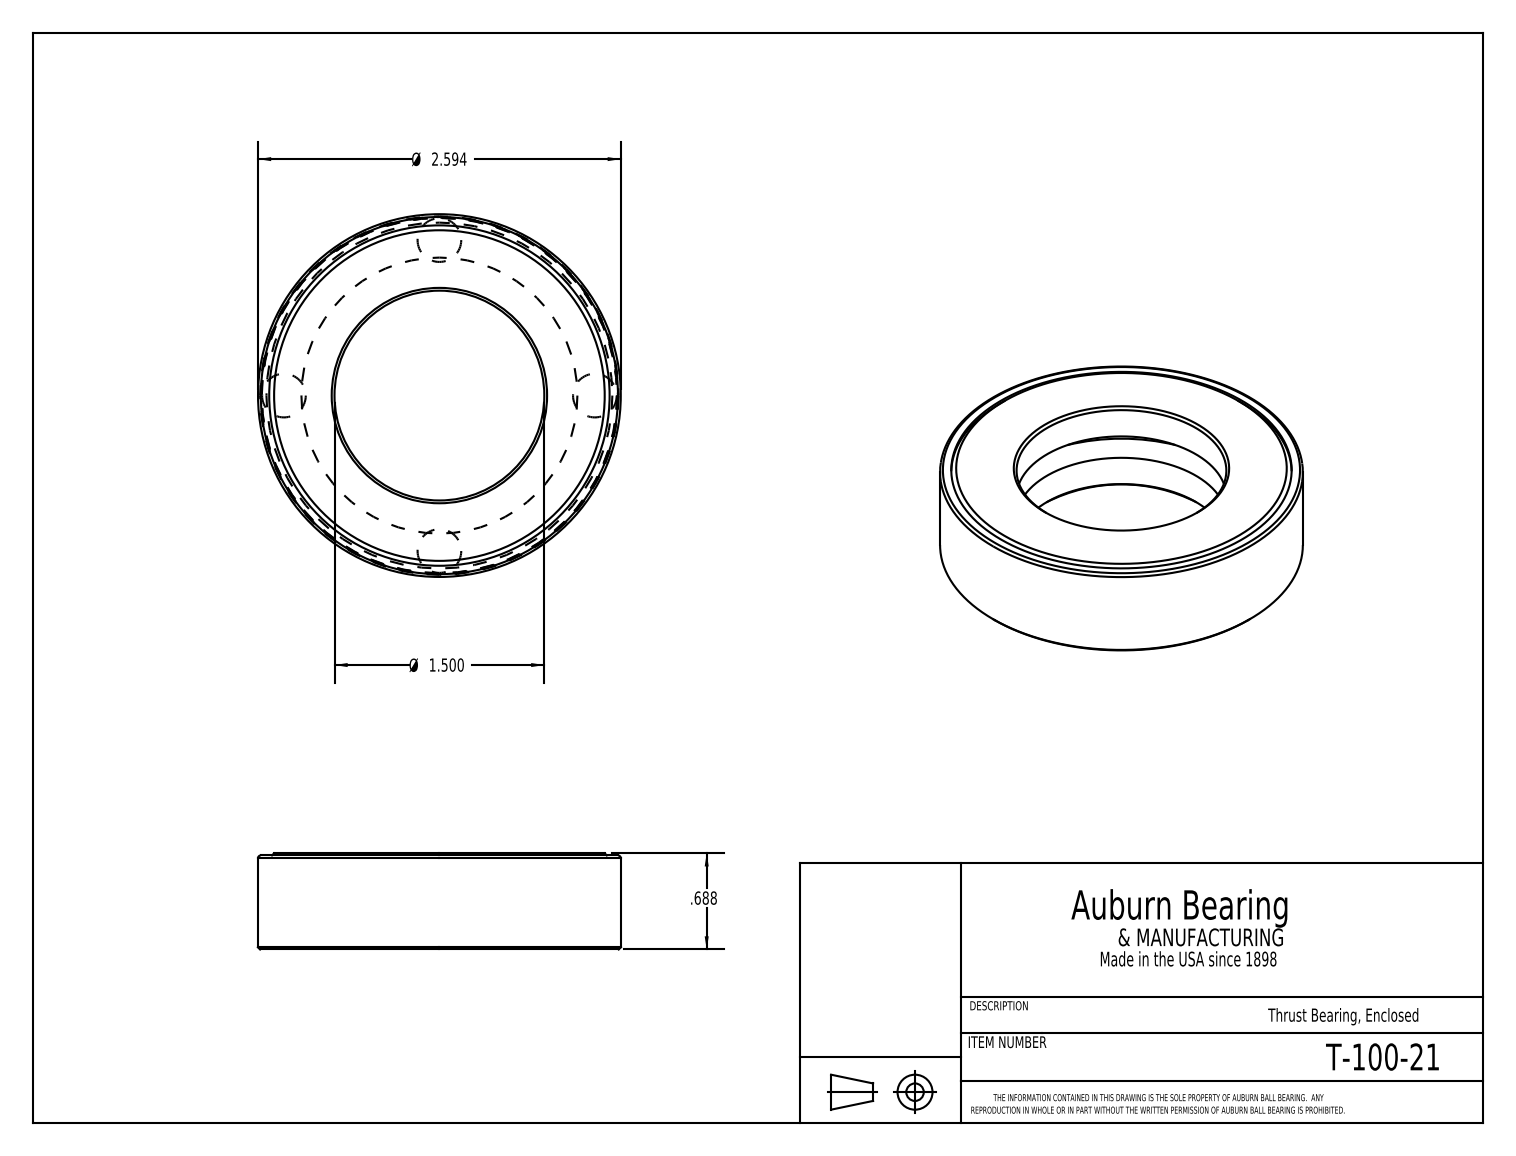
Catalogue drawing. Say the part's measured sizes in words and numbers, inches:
The part is named "T-100-21". Its 3-D file was written by "SolidWorks 2016 (CONFIG_CONTROL_DESIGN)". It is 6 solids with 28 faces: 9 planar, 7 cylindrical and 12 other. Overall it measures 2.594 by 2.594 by 0.688 inches. Its volume is 1.659 cubic inches and its surface area 28.95 square inches. Round holes: 1 of diameter 1.5, 1 of diameter 2.434, 1 of diameter 2.554. Round bosses or shafts: 1 of diameter 2.594, 1 of diameter 2.54. The main face-to-face distances are 0.25, 0.437, 0.687, 0.187, 0.652, 0.402, 0.215, 0.035, 0.672, 0.422.
